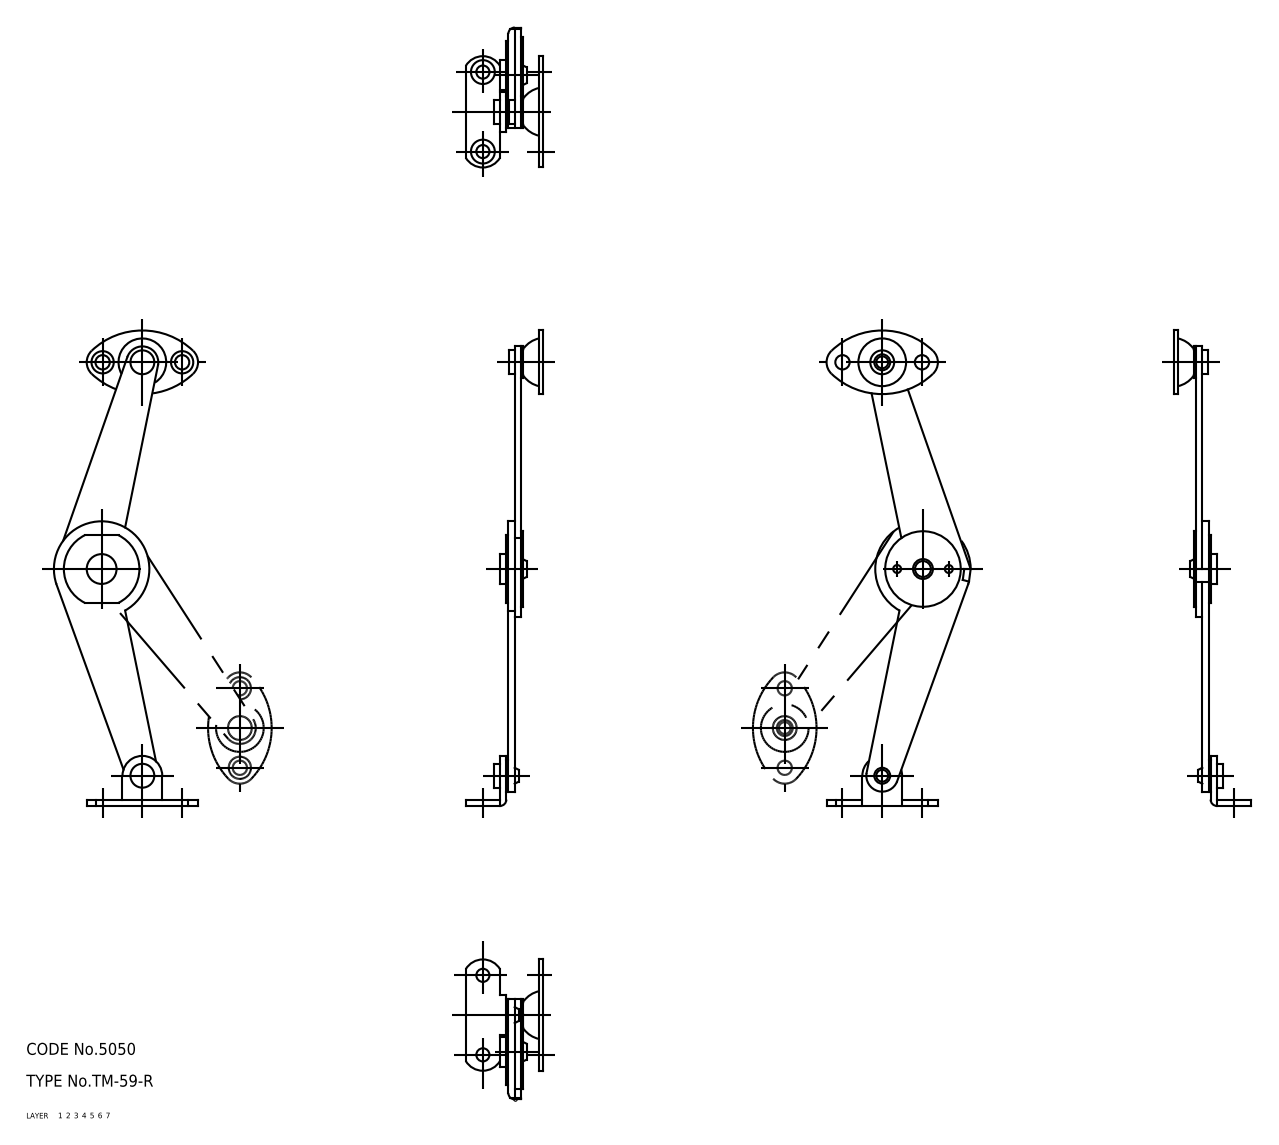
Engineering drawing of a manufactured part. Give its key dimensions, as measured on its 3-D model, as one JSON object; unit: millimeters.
{"part_name": "rivet_B2_mr; rivet_B1_mr; washer_mr-1; washer_mr (+8 more)", "step_written_by": "CADfix (AUTOMOTIVE_DESIGN)", "units": "millimeters", "bodies": {"solids": 12, "faces": 135, "planar": 0, "cylindrical": 0, "other": 135}, "overall_size": [119.6, 36.25, 19.4], "volume_mm3": 4273, "surface_area_mm2": 7131}
